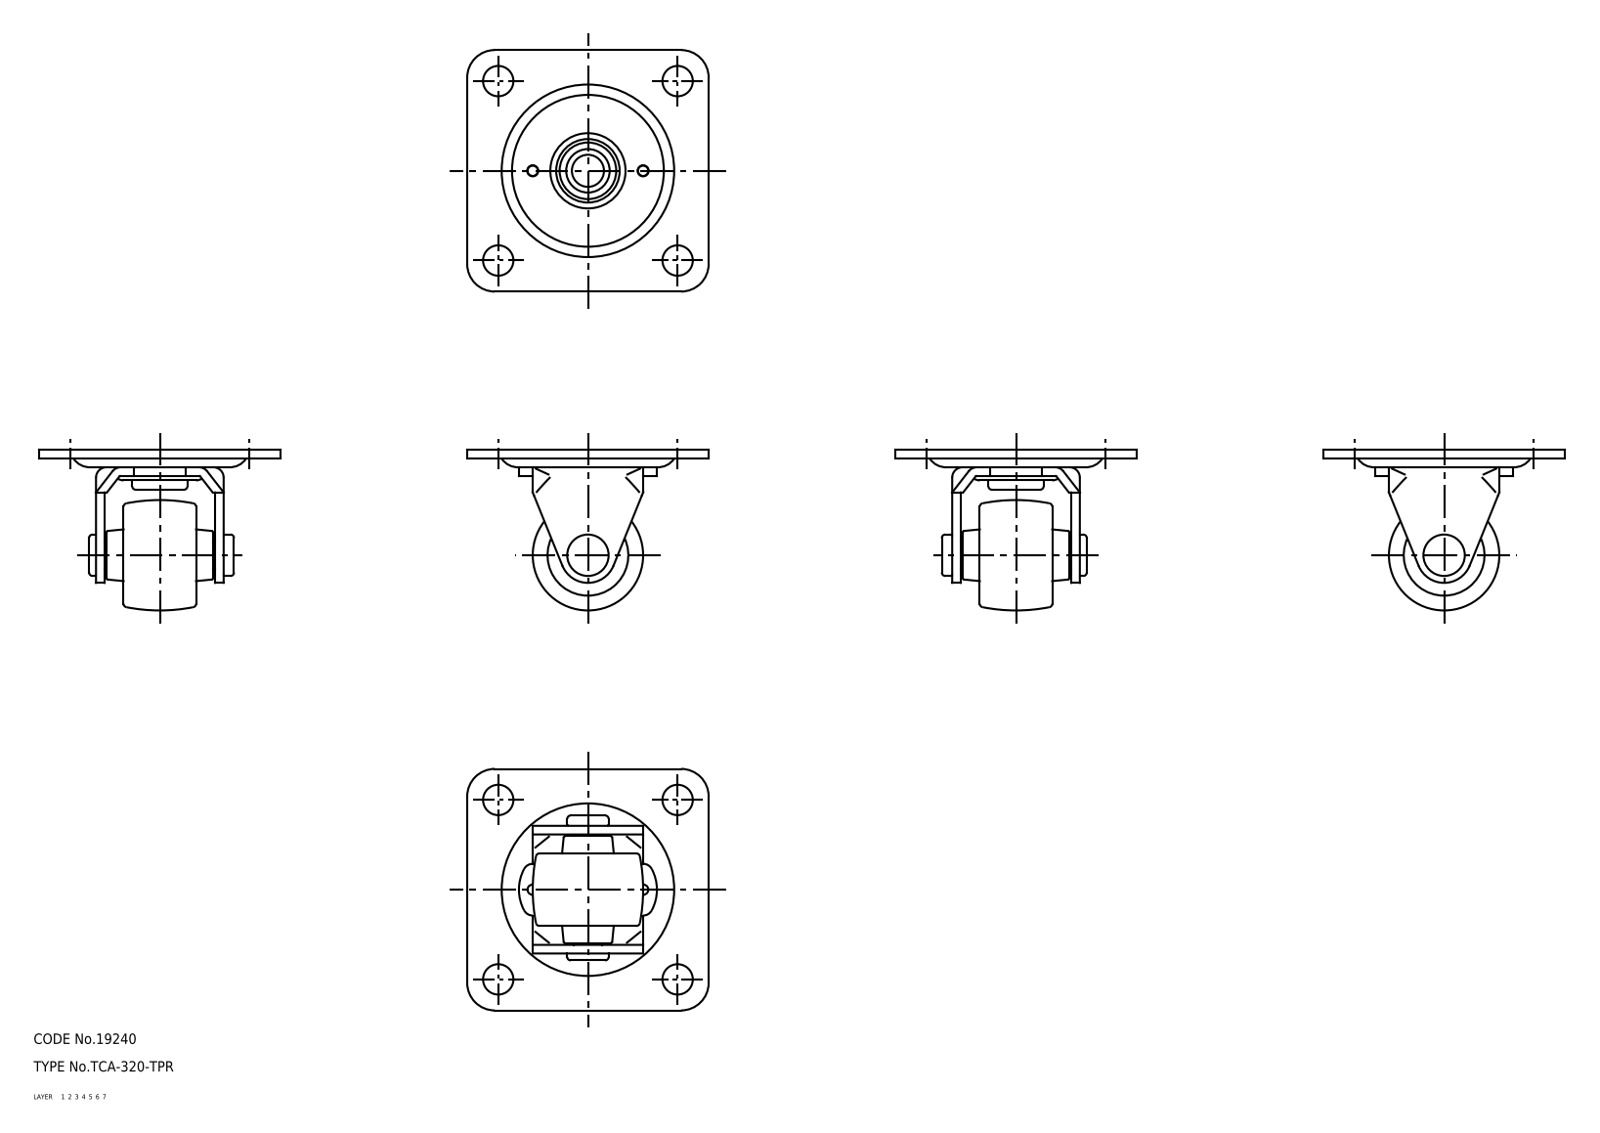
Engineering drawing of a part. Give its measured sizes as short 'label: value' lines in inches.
name: wheel; mounting plate; main shaft; axle (+1 more)
written by: CADfix (AUTOMOTIVE_DESIGN)
unit: in
bodies: 5 solids, 174 faces (0 planar, 0 cylindrical, 174 other)
size: 2.756 × 2.756 × 1.831
volume: 2.195 in³; area: 36.26 in²
